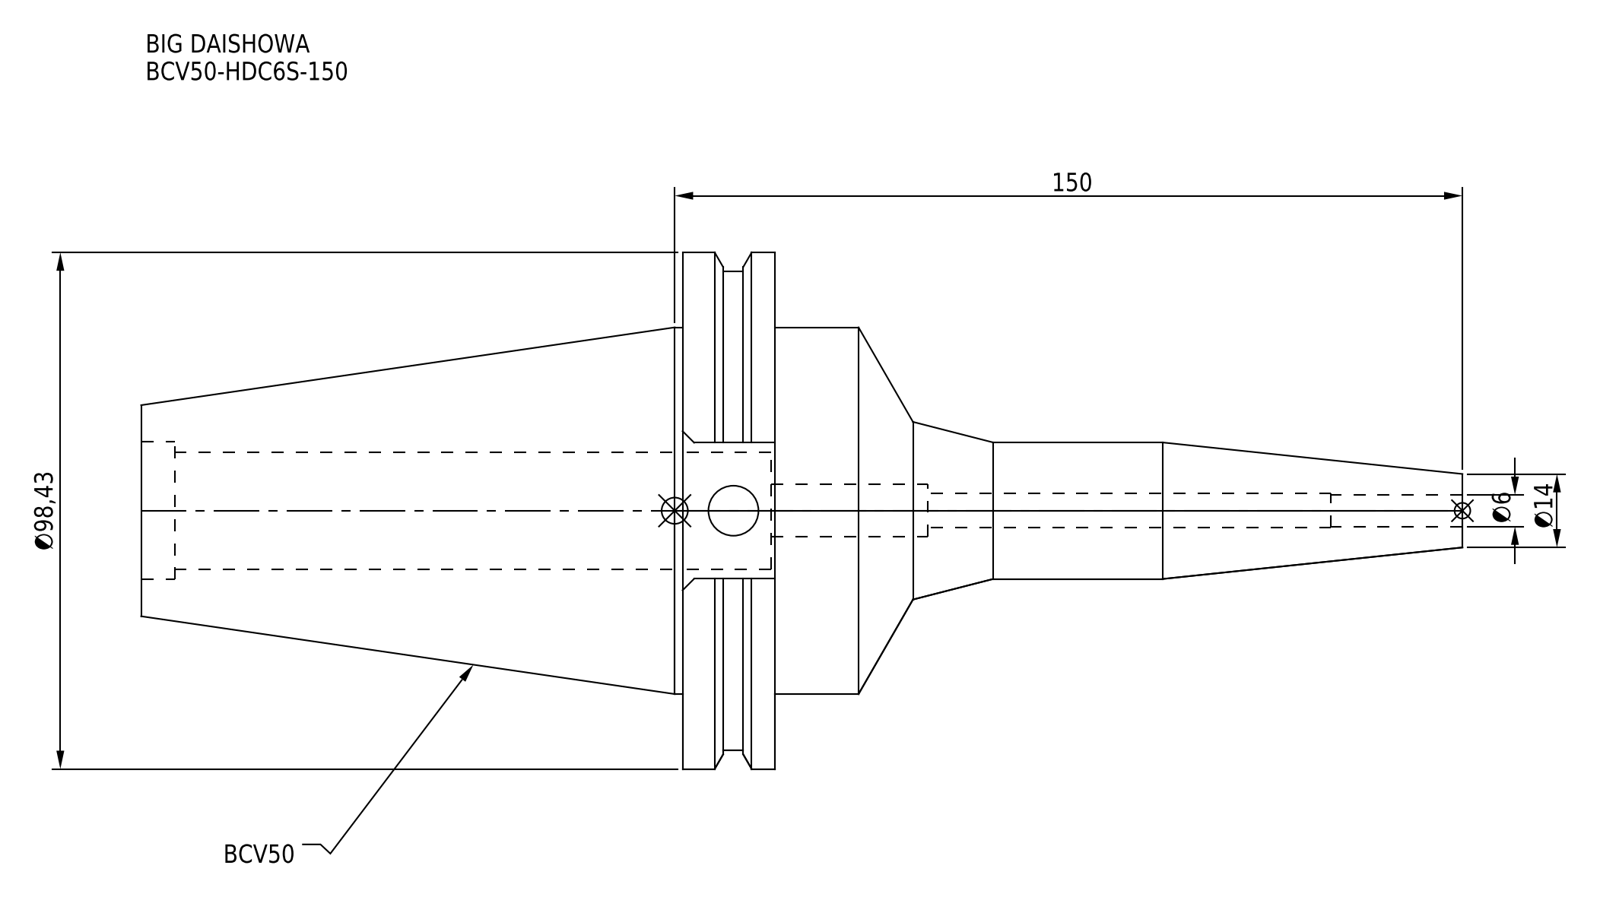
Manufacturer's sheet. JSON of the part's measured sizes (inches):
{"part_name": "BCV50-HDC6S-150", "step_written_by": "CREO PARAMETRIC BY PTC INC, 2016380 (AUTOMOTIVE_DESIGN)", "units": "inches", "bodies": {"solids": 1, "faces": 61, "planar": 23, "cylindrical": 26, "other": 12}, "overall_size": [9.906, 3.875, 3.738], "volume_in3": 27.34, "surface_area_in2": 91.34, "round_holes": [[0.236, 1], [0.256, 1], [0.375, 1], [0.394, 1], [0.878, 1], [1.033, 1]], "round_bosses_or_shafts": [[3.875, 1], [3.594, 1], [2.75, 1], [1.024, 1]], "face_to_face_distances": [0.691, 4.75, 4.059, 2.872, 0.026, 0.665, 4.724, 1.02, 0.236, 0.211]}
